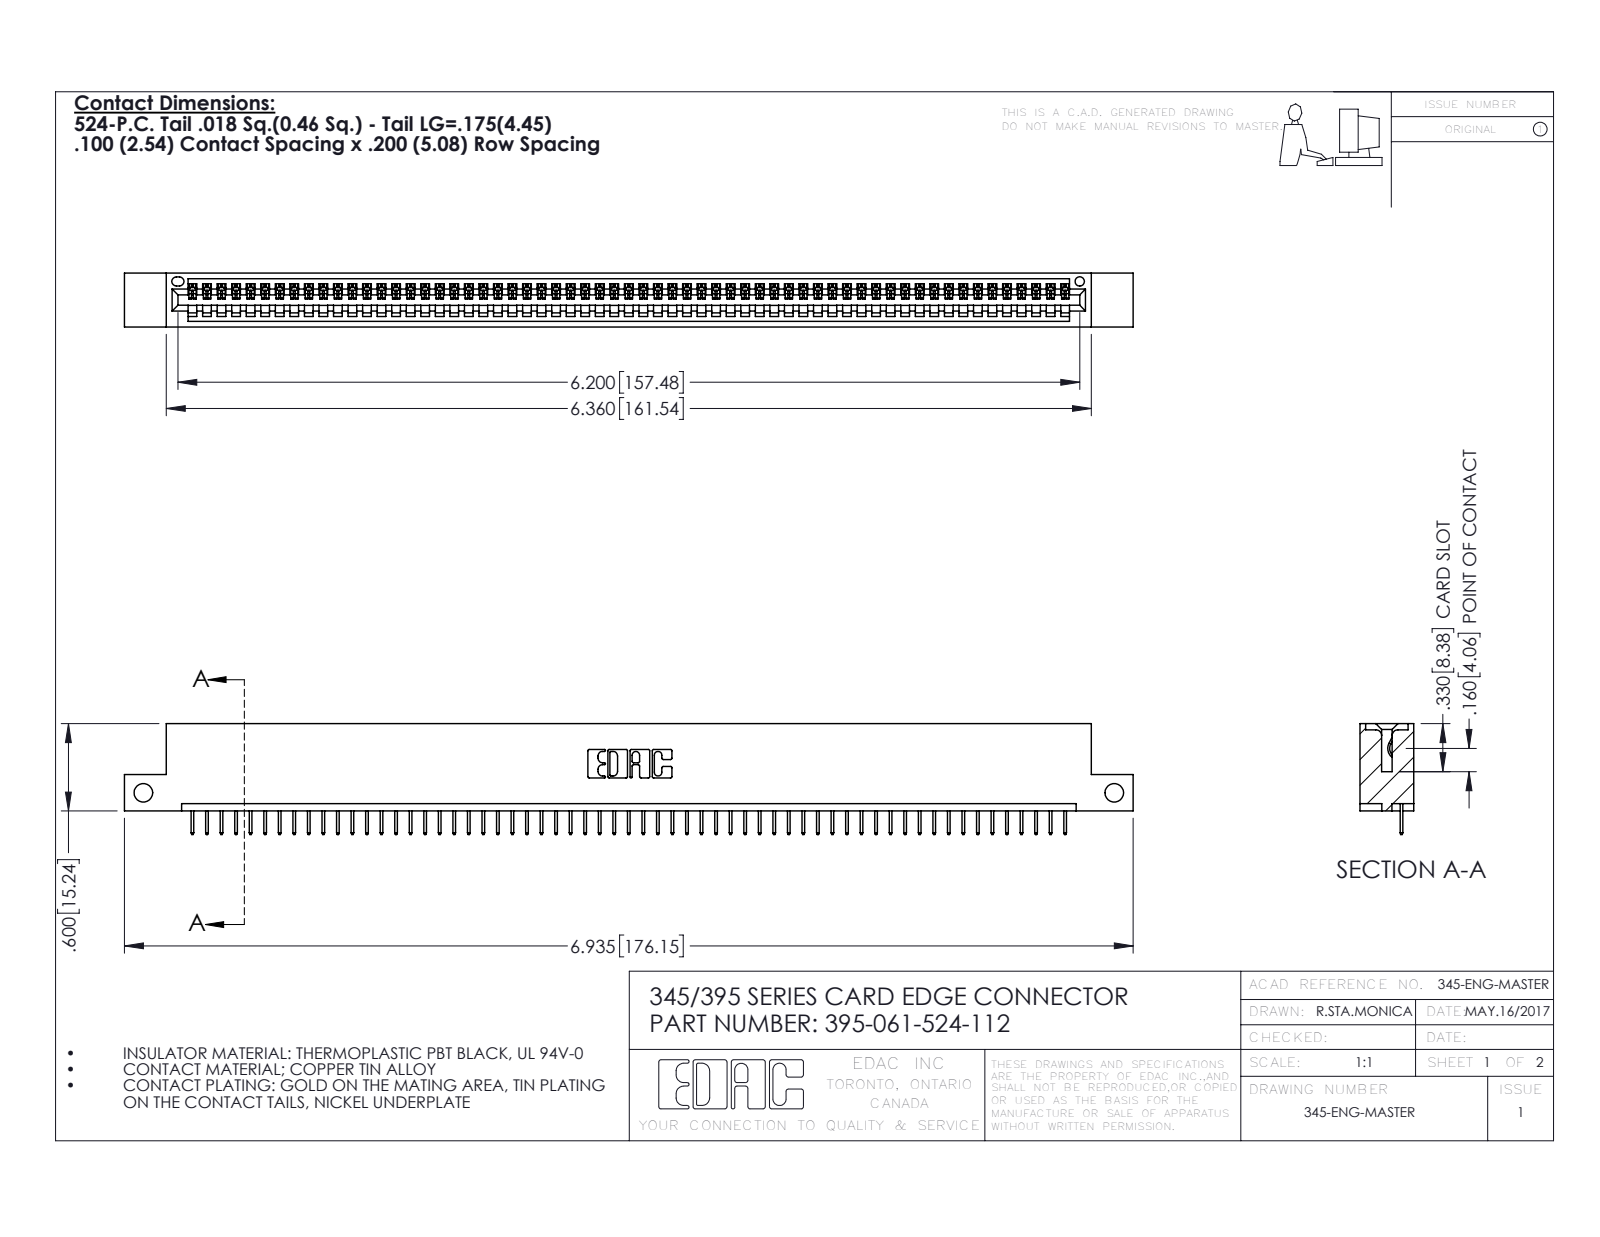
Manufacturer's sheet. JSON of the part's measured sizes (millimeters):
{"part_name": "345 Part_Flush Mounting Lugs - Side Mount; 395-061-524-112; 345-292-001_345-293-124", "step_written_by": "SolidWorks 2016 (CONFIG_CONTROL_DESIGN)", "units": "millimeters", "bodies": {"solids": 62, "faces": 3908, "planar": 2886, "cylindrical": 1022, "other": 0}, "overall_size": [176.1, 19.4, 9.4], "volume_mm3": 16550, "surface_area_mm2": 21350, "round_holes": [[3.3, 2], [1.6, 1]], "partial_cylinders_radius": [[0.2, 122], [0.3, 22], [0.2, 6], [0.8, 6], [0.7, 3], [0.8, 2], [1, 2], [0.4, 1]], "face_to_face_distances": [7.6, 1.8, 9.4, 5.1, 2.5, 6.9, 0.6, 5.7, 1.8, 3.8], "hole_center_spacings": [169.5]}
